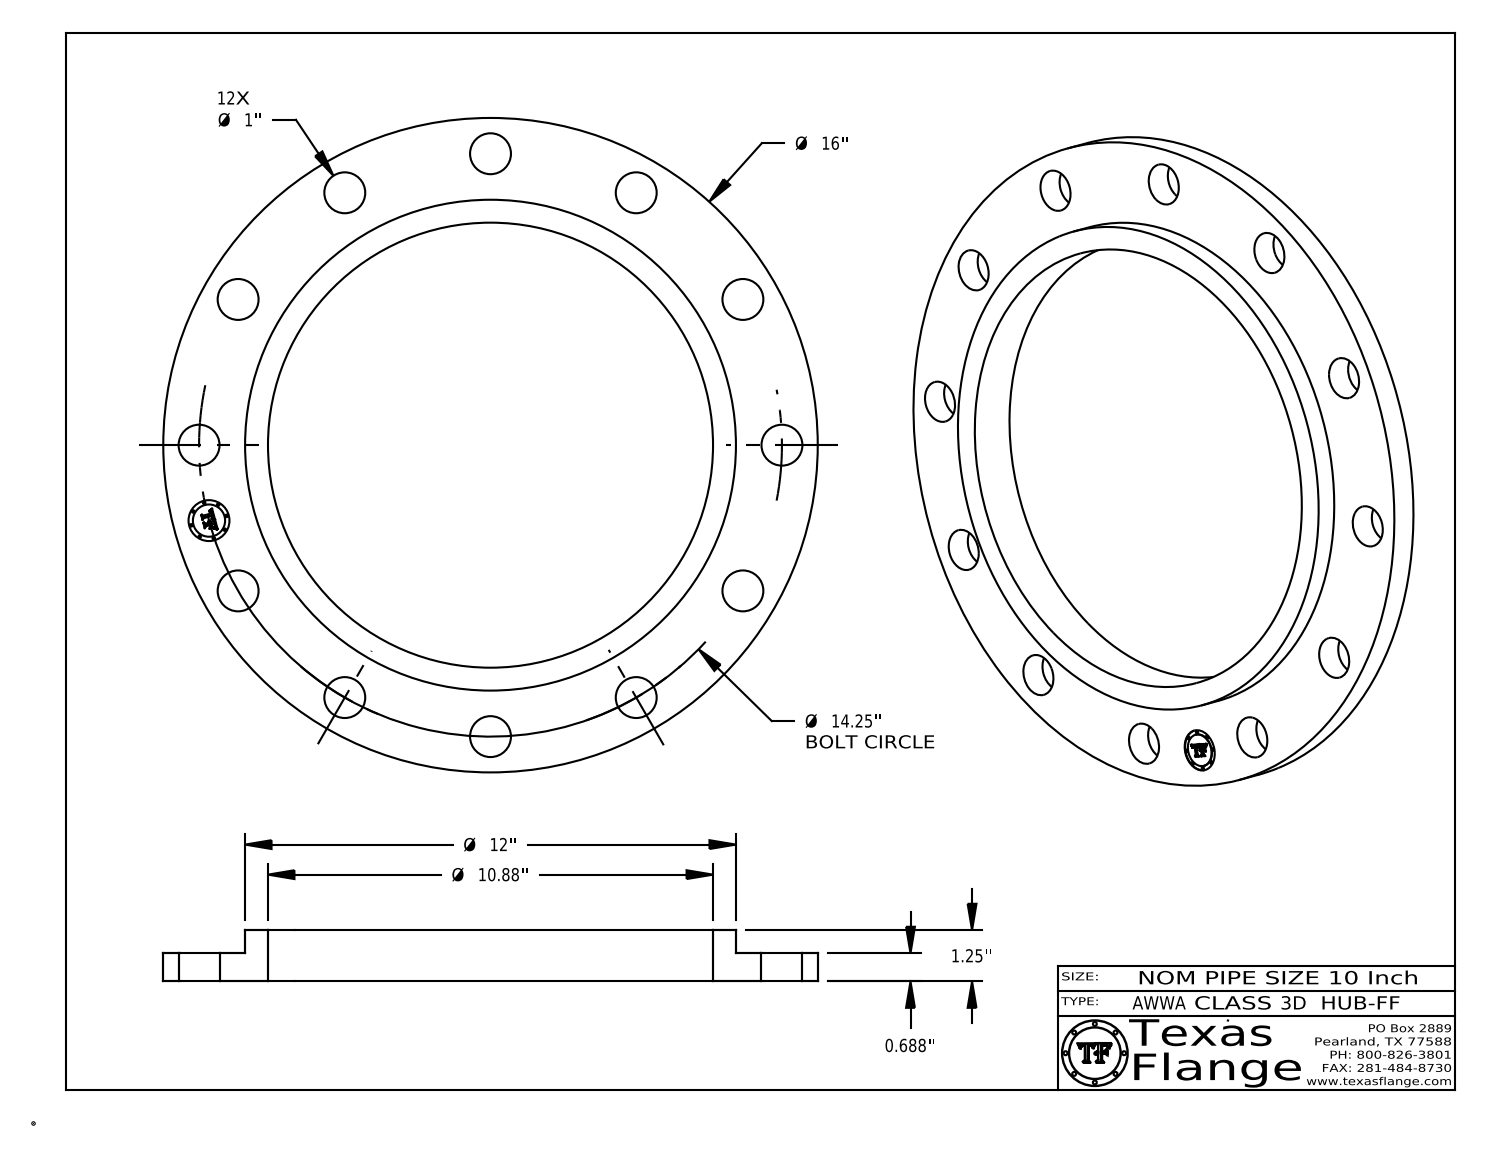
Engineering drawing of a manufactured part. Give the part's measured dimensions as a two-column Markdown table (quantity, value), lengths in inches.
| quantity | value |
| --- | --- |
| part name | AWWA Class 3D-HUB-FF |
| STEP written by | CATIA V5 STEP AP214 (AUTOMOTIVE_DESIGN) |
| units | inches |
| bodies | 1 solid, 418 faces (368 planar, 50 cylindrical, 0 other) |
| overall size | 16 × 16 × 1.25 |
| volume | 79.19 in³ |
| surface area | 322 in² |
| round holes (diameter × count) | 1 × 13, 10.88 × 1 |
| round bosses / shafts (diameter × count) | 0.061 × 8, 16 × 1, 12 × 1, 0.788 × 1 |
| main face-to-face distances | 0.688, 1.25, 0.562, 0.673, 0.015, 0.577, 0.298, 0.292, 0.019, 0.054 |
| hole center spacings | 7.125, 3.688, 10.076, 12.341, 13.765, 14.25, 11.306, 13.165 |
